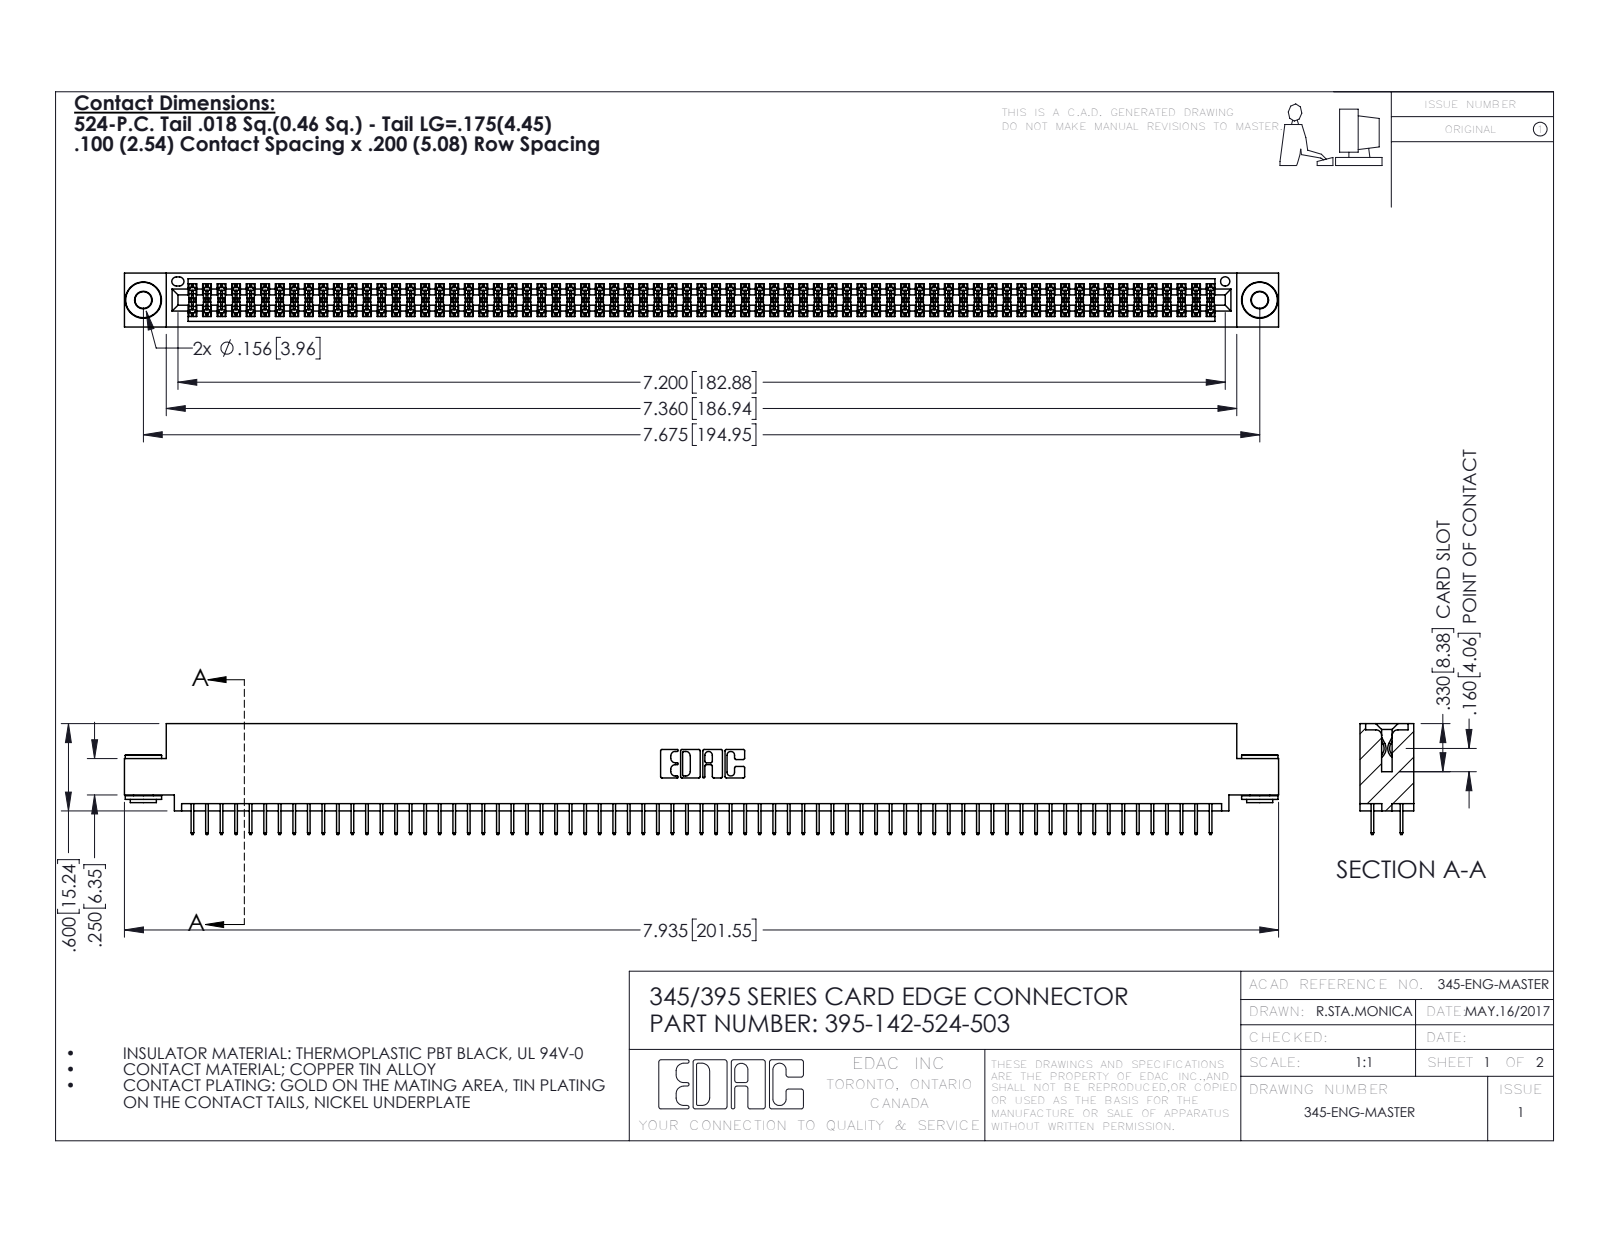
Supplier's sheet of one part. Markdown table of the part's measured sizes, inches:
| quantity | value |
| --- | --- |
| part name | 345-250-002_345-250-002-102; 345 Part_0.110 Offset - 0.156 Dia-TH; 395-142-524-503; 345-292-001_345-293-124 |
| STEP written by | SolidWorks 2016 (CONFIG_CONTROL_DESIGN) |
| units | inches |
| bodies | 145 solids, 7836 faces (5632 planar, 2196 cylindrical, 8 other) |
| overall size | 7.935 × 0.762 × 0.37 |
| volume | 1.195 in³ |
| surface area | 45.31 in² |
| round holes (diameter × count) | 0.116 × 2, 0.156 × 2, 0.064 × 1 |
| round bosses / shafts (diameter × count) | 0.25 × 2, 0.18 × 2, 0.136 × 2 |
| partial cylindrical surfaces (radius × count) | 0.006 × 213, 0.01 × 22, 0.007 × 6, 0.031 × 6, 0.026 × 3, 0.014 × 2, 0.019 × 2, 0.022 × 2 |
| main face-to-face distances | 0.072, 0.298, 0.2, 0.37, 0.025, 0.098, 0.272, 0.225, 0.072, 0.175 |
| hole center spacings | 0.27, 7.439, 7.675 |
